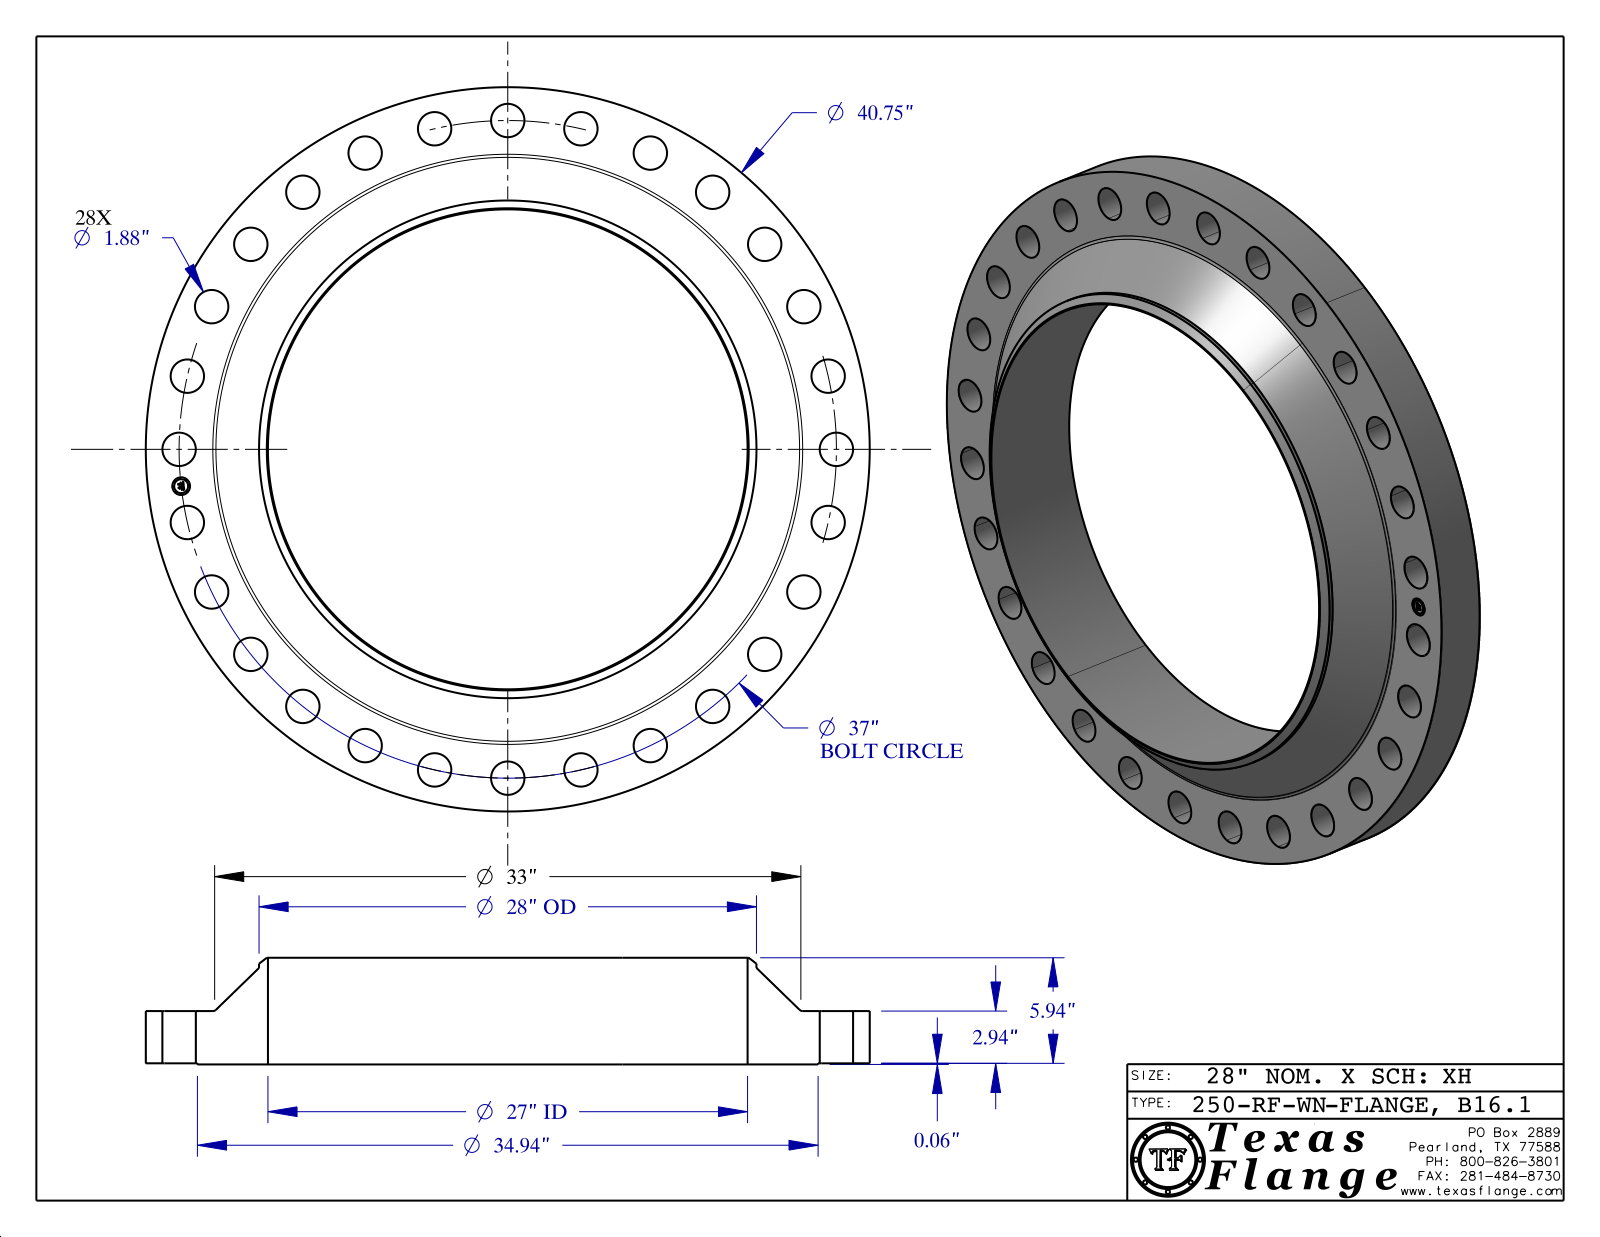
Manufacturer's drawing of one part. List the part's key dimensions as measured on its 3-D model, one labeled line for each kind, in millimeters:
Part name (STEP PRODUCT): 250-RF-WN, B16.1
STEP written by: CATIA V5 STEP AP203 (CONFIG_CONTROL_DESIGN)
Units: millimetres
Bodies: 1 solid, 459 faces (369 planar, 84 cylindrical, 6 other)
Overall size (bounding box): 1035.05 × 1035.05 × 152.46
Volume: 38 560 000 mm³ · Surface area: 1 813 000 mm²
Round holes (diameter × count): ⌀47.75 ×28, ⌀25.4 ×1, ⌀685.8 ×1
Round bosses / shafts (diameter × count): ⌀1.54 ×8, ⌀1035.05 ×1, ⌀887.48 ×1, ⌀711.2 ×1, ⌀20.01 ×1
Main face-to-face distances: 76.27, 1.59, 74.68, 152.47, 150.88, 76.2, 0.38, 75.89, 74.3, 76.58
Hole centre spacings: 469.9, 664.54, 795.75, 916.24, 933.89, 846.73, 105.22, 407.76
